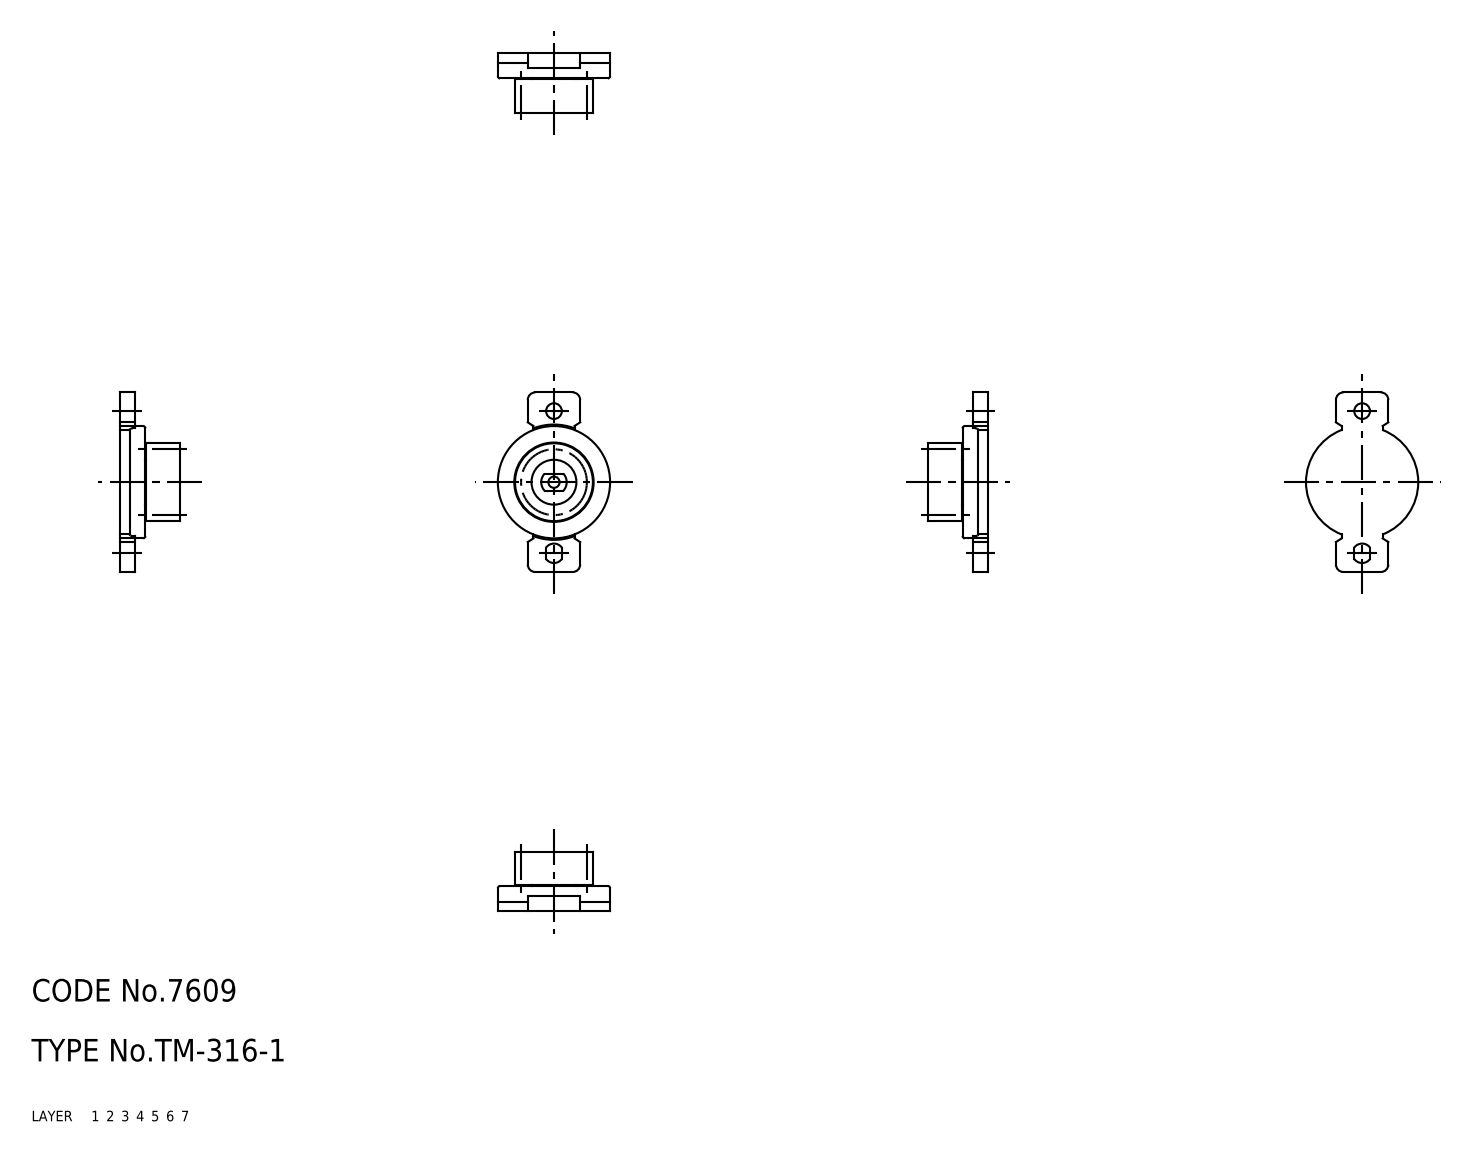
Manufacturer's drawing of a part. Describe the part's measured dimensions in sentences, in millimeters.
The part is named "67114042; 67114055". Its 3-D file was written by "CADfix (AUTOMOTIVE_DESIGN)". It is 2 solids with 101 faces: 0 planar, 0 cylindrical and 101 other. Overall it measures 24 by 15 by 8 millimeters. Its volume is 949 cubic millimeters and its surface area 1 246 square millimeters.
